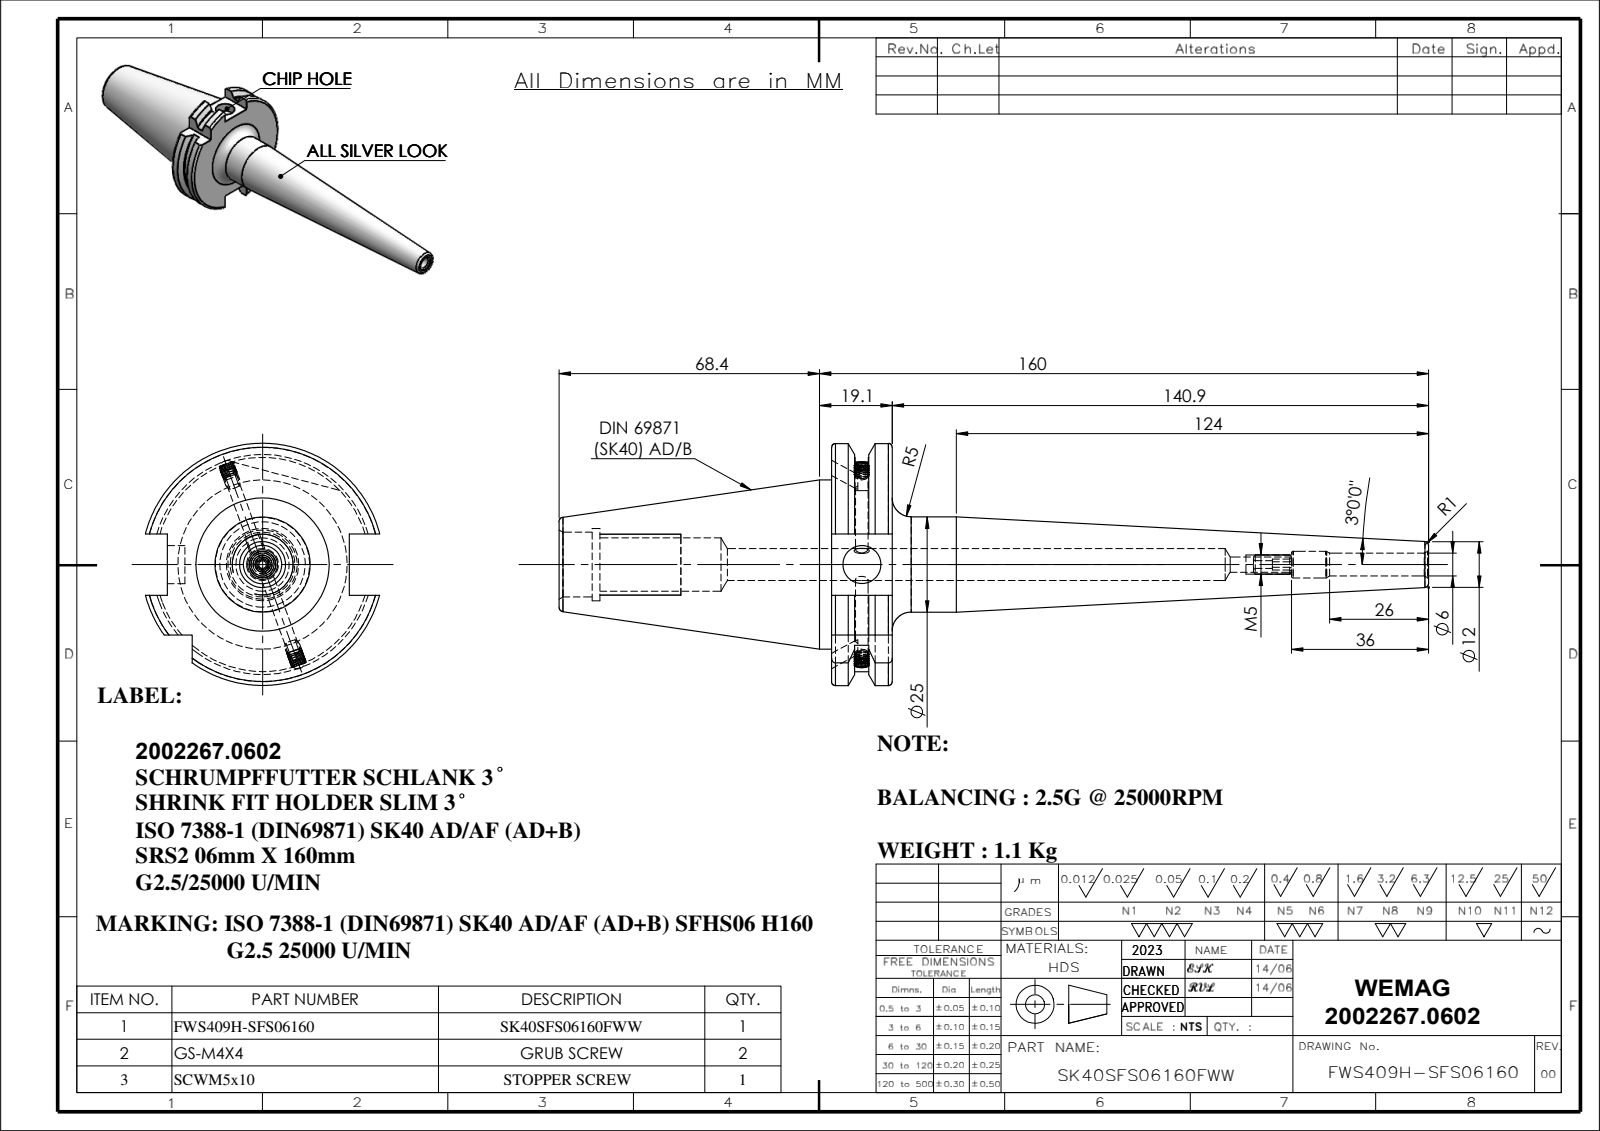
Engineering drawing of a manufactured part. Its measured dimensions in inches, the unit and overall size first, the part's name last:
Units: inches
Overall size (bounding box): 8.992 × 2.502 × 2.42
Round holes (diameter × count): ⌀0.079 ×1, ⌀0.13 ×1, ⌀0.157 ×1, ⌀0.236 ×1, ⌀0.276 ×1, ⌀0.331 ×1, ⌀0.394 ×1, ⌀0.551 ×1, ⌀0.669 ×1, ⌀0.748 ×1
Round bosses / shafts (diameter × count): ⌀0.157 ×2, ⌀1.75 ×1, ⌀0.984 ×1, ⌀0.197 ×1
Partial cylindrical surfaces — rounded edges, fillets, slot ends (radius × count): R1.107 ×1, R1.251 ×1
Main face-to-face distances: 0.626, 0.634, 1.882, 2.819, 3.445, 0.421, 2.398, 3.024, 3.056, 2.635
Volume: 8.547 in³ · Surface area: 50.3 in²
Bodies: 4 solids, 230 faces (62 planar, 60 cylindrical, 108 other)
Part name (STEP PRODUCT): SK40SFS06160FWW; SCWM5X10; 91406-SRS206160; GS-M4X4_DIN 913 - M4 x 4-N
STEP written by: SolidWorks 2018 (CONFIG_CONTROL_DESIGN)
